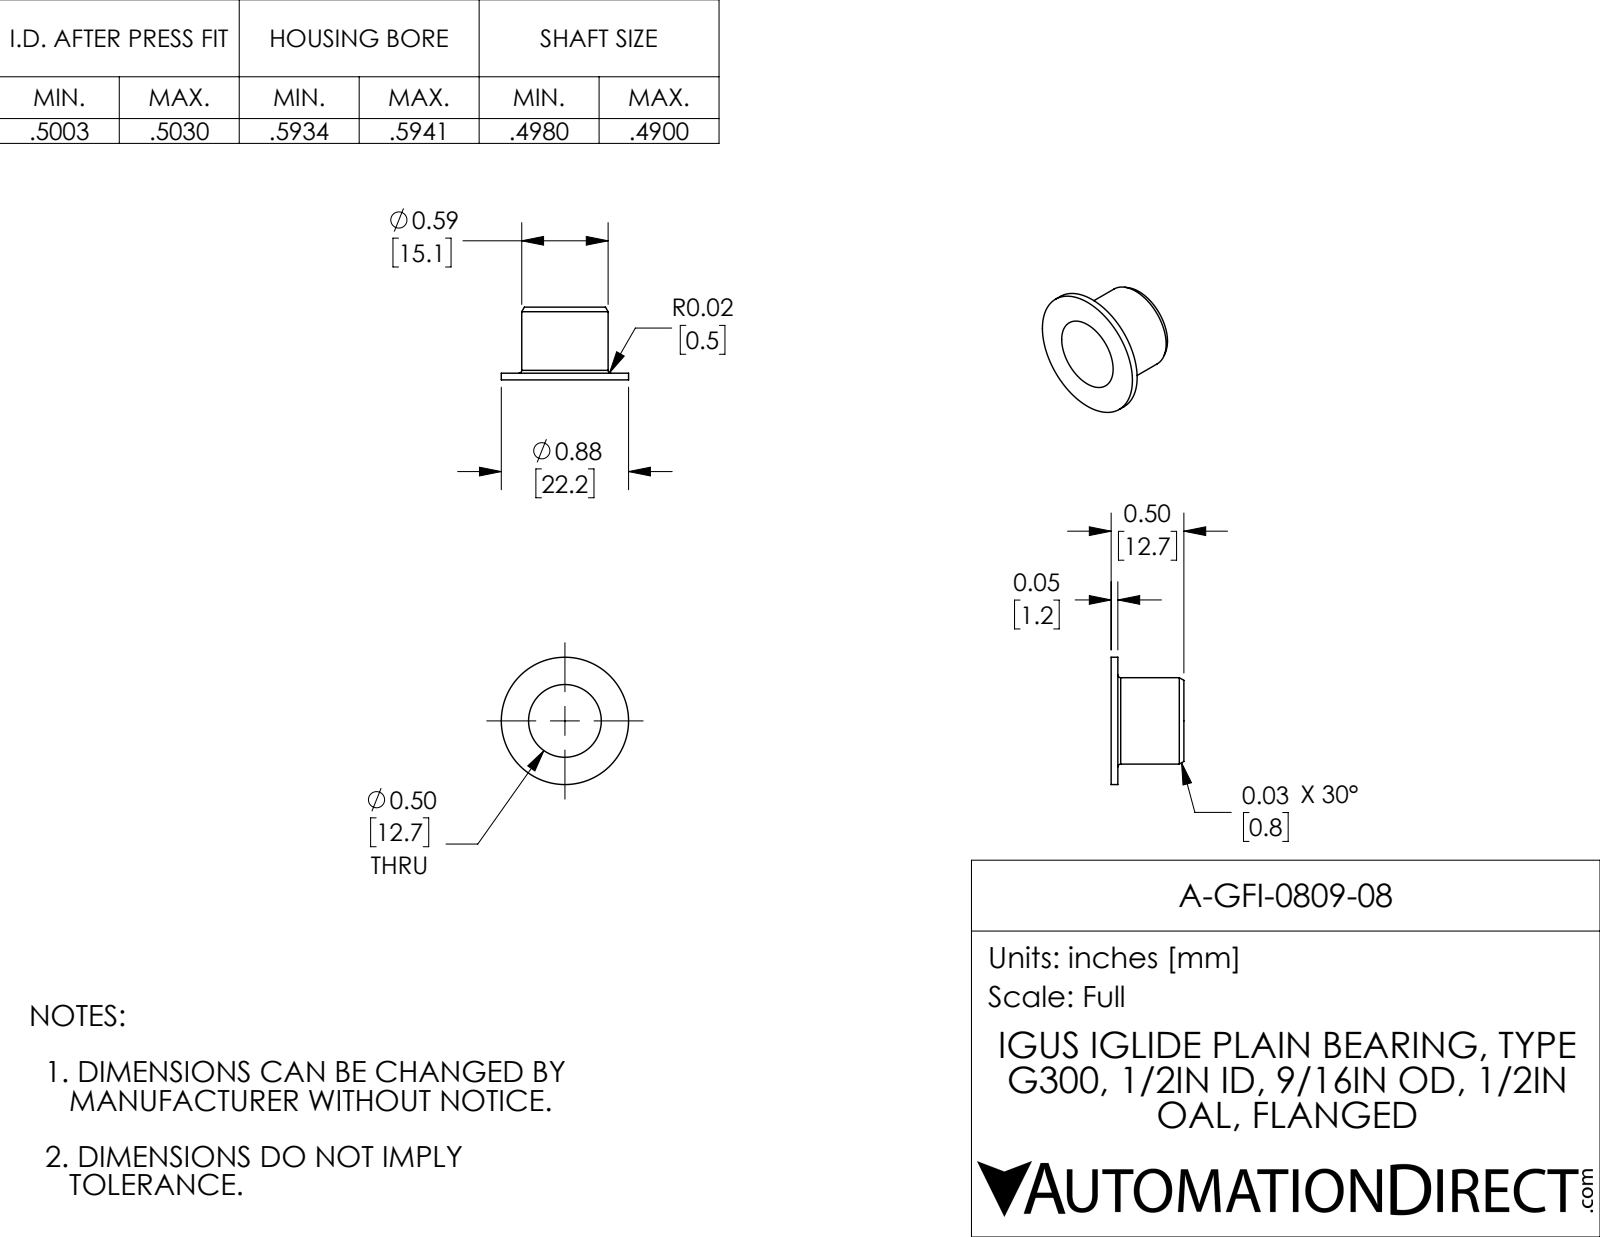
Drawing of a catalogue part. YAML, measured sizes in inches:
part_name: "A-GFI-0809-08"
step_written_by: "SolidWorks 2017 (AUTOMOTIVE_DESIGN)"
units: inches
bodies: {solids: 1, faces: 13, planar: 3, cylindrical: 6, other: 4}
overall_size: [0.875, 0.875, 0.5]
volume: 0.055
surface_area: 2.527
round_holes:
  - {diameter: 0.5, count: 1}
round_bosses_or_shafts:
  - {diameter: 0.875, count: 1}
  - {diameter: 0.594, count: 1}
face_to_face_distances: [0.046, 0.5, 0.454]
